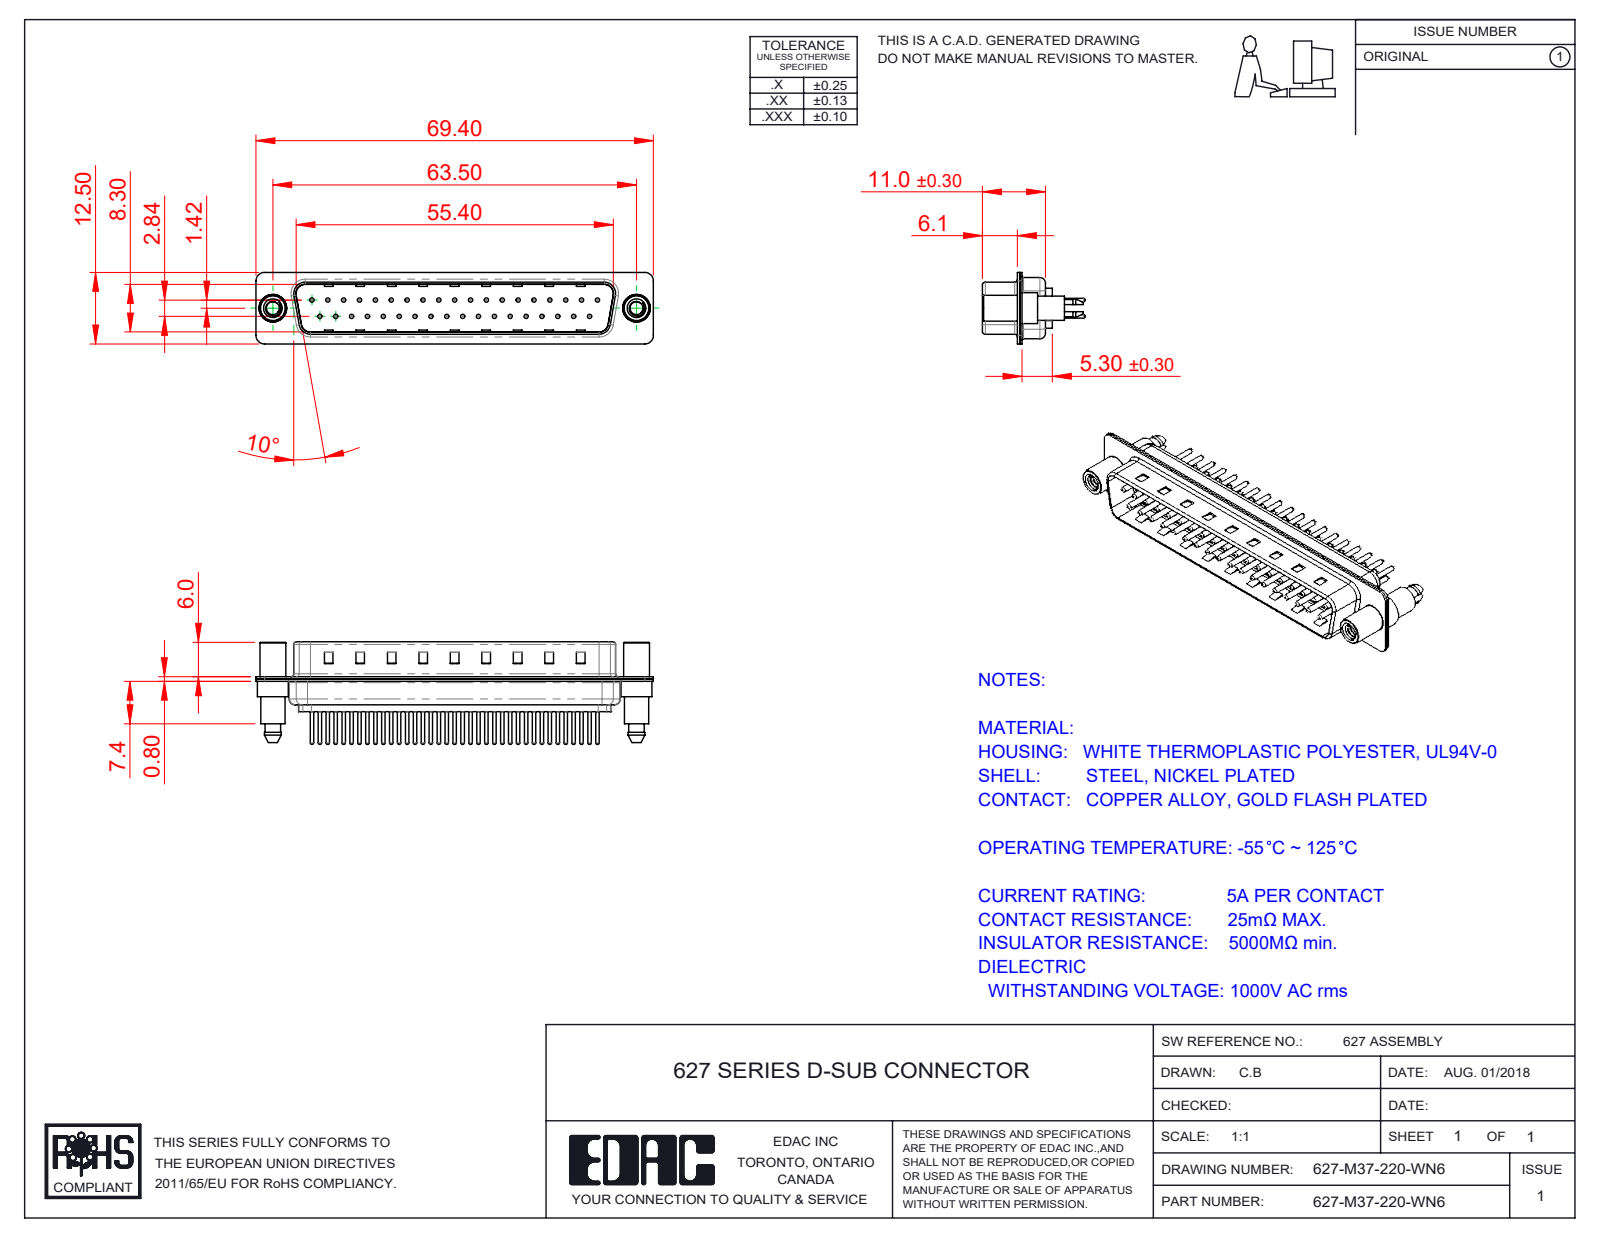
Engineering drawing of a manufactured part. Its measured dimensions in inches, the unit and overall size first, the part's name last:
Units: inches
Overall size (bounding box): 2.732 × 0.705 × 0.492
Round holes (diameter × count): ⌀0.03 ×37, ⌀0.063 ×37, ⌀0.079 ×37, ⌀0.089 ×2, ⌀0.157 ×2, ⌀0.189 ×2
Round bosses / shafts (diameter × count): ⌀0.059 ×37, ⌀0.024 ×37, ⌀0.213 ×2, ⌀0.193 ×2, ⌀0.177 ×2, ⌀0.167 ×2
Partial cylindrical surfaces — rounded edges, fillets, slot ends (radius × count): R0.059 ×18, R0.079 ×12, R0.063 ×10, R0.02 ×8, R0.01 ×4, R0.024 ×4, R0.026 ×4, R0.035 ×4
Main face-to-face distances: 0.016, 0.031, 0.374, 0.358, 0.343, 0.39, 0.047, 0.224, 0.03, 0.014
Hole centre spacings: 0.109, 0.218, 0.124, 0.327, 0.436, 0.545, 0.654, 0.763
Volume: 0.251 in³ · Surface area: 15.09 in²
Bodies: 42 solids, 1833 faces (480 planar, 687 cylindrical, 666 other)
Part name (STEP PRODUCT): 627M Contact Row 2_20; 627-M37-220-WN6; 627M Housing_37 Contacts; 627M Shell Front_37 Contacts (+3 more)
STEP written by: SolidWorks 2020 (CONFIG_CONTROL_DESIGN)
